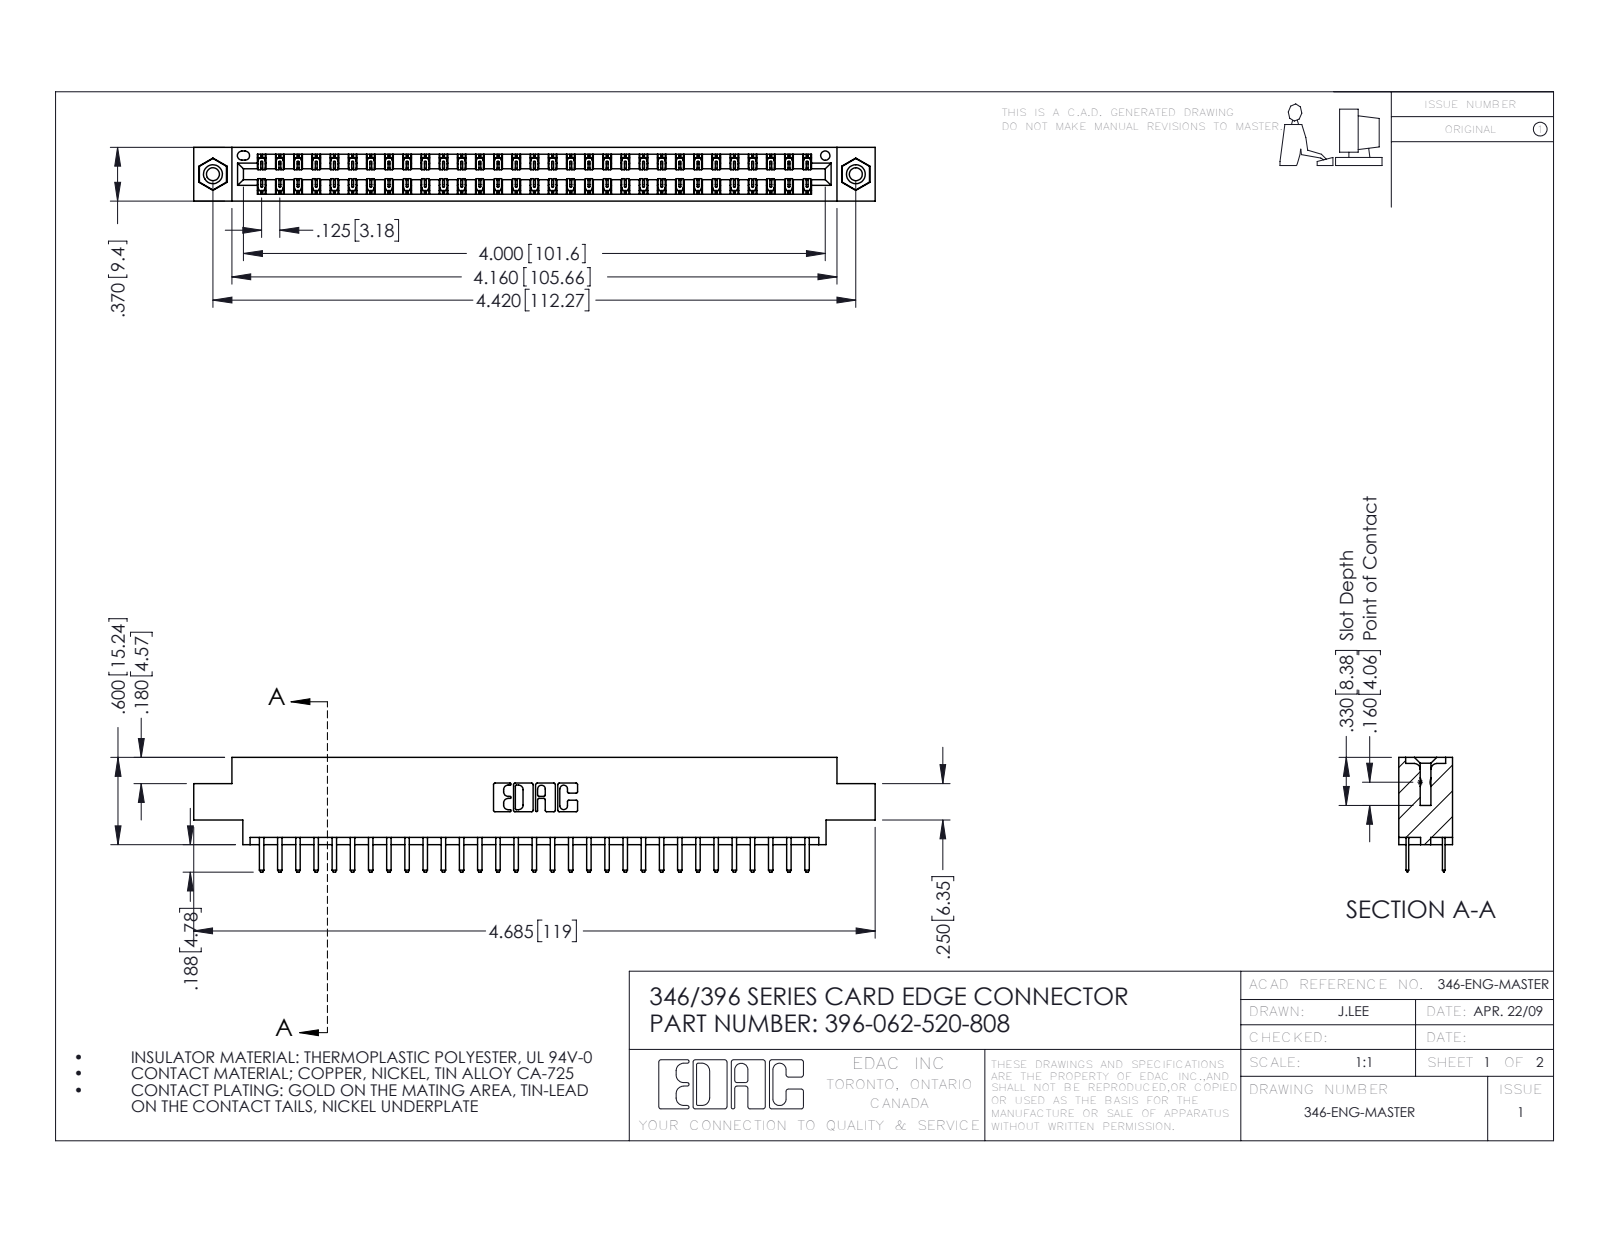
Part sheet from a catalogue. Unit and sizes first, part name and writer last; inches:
Units: inches
Overall size (bounding box): 4.685 × 0.788 × 0.37
Round holes (diameter × count): ⌀0.089 ×2, ⌀0.125 ×2, ⌀0.156 ×2, ⌀0.064 ×1
Round bosses / shafts (diameter × count): ⌀0.155 ×2
Partial cylindrical surfaces — rounded edges, fillets, slot ends (radius × count): R0.006 ×93, R0.01 ×66, R0.01 ×22, R0.007 ×6, R0.031 ×6, R0.026 ×3, R0.014 ×2, R0.022 ×2
Main face-to-face distances: 0.048, 0.322, 0.25, 0.37, 0.275, 0.072, 0.298, 0.025, 0.222, 0.148
Hole centre spacings: 0.246, 4.212, 4.42
Volume: 0.691 in³ · Surface area: 24.08 in²
Bodies: 65 solids, 3658 faces (2406 planar, 1236 cylindrical, 16 other)
Part name (STEP PRODUCT): 396-062-520-808; 346 Part_0.170 Offset - 0.156 Dia-TI; 345-292-001_345-293-120; 345-250-001_345-250-003-102
STEP written by: SolidWorks 2016 (CONFIG_CONTROL_DESIGN)
